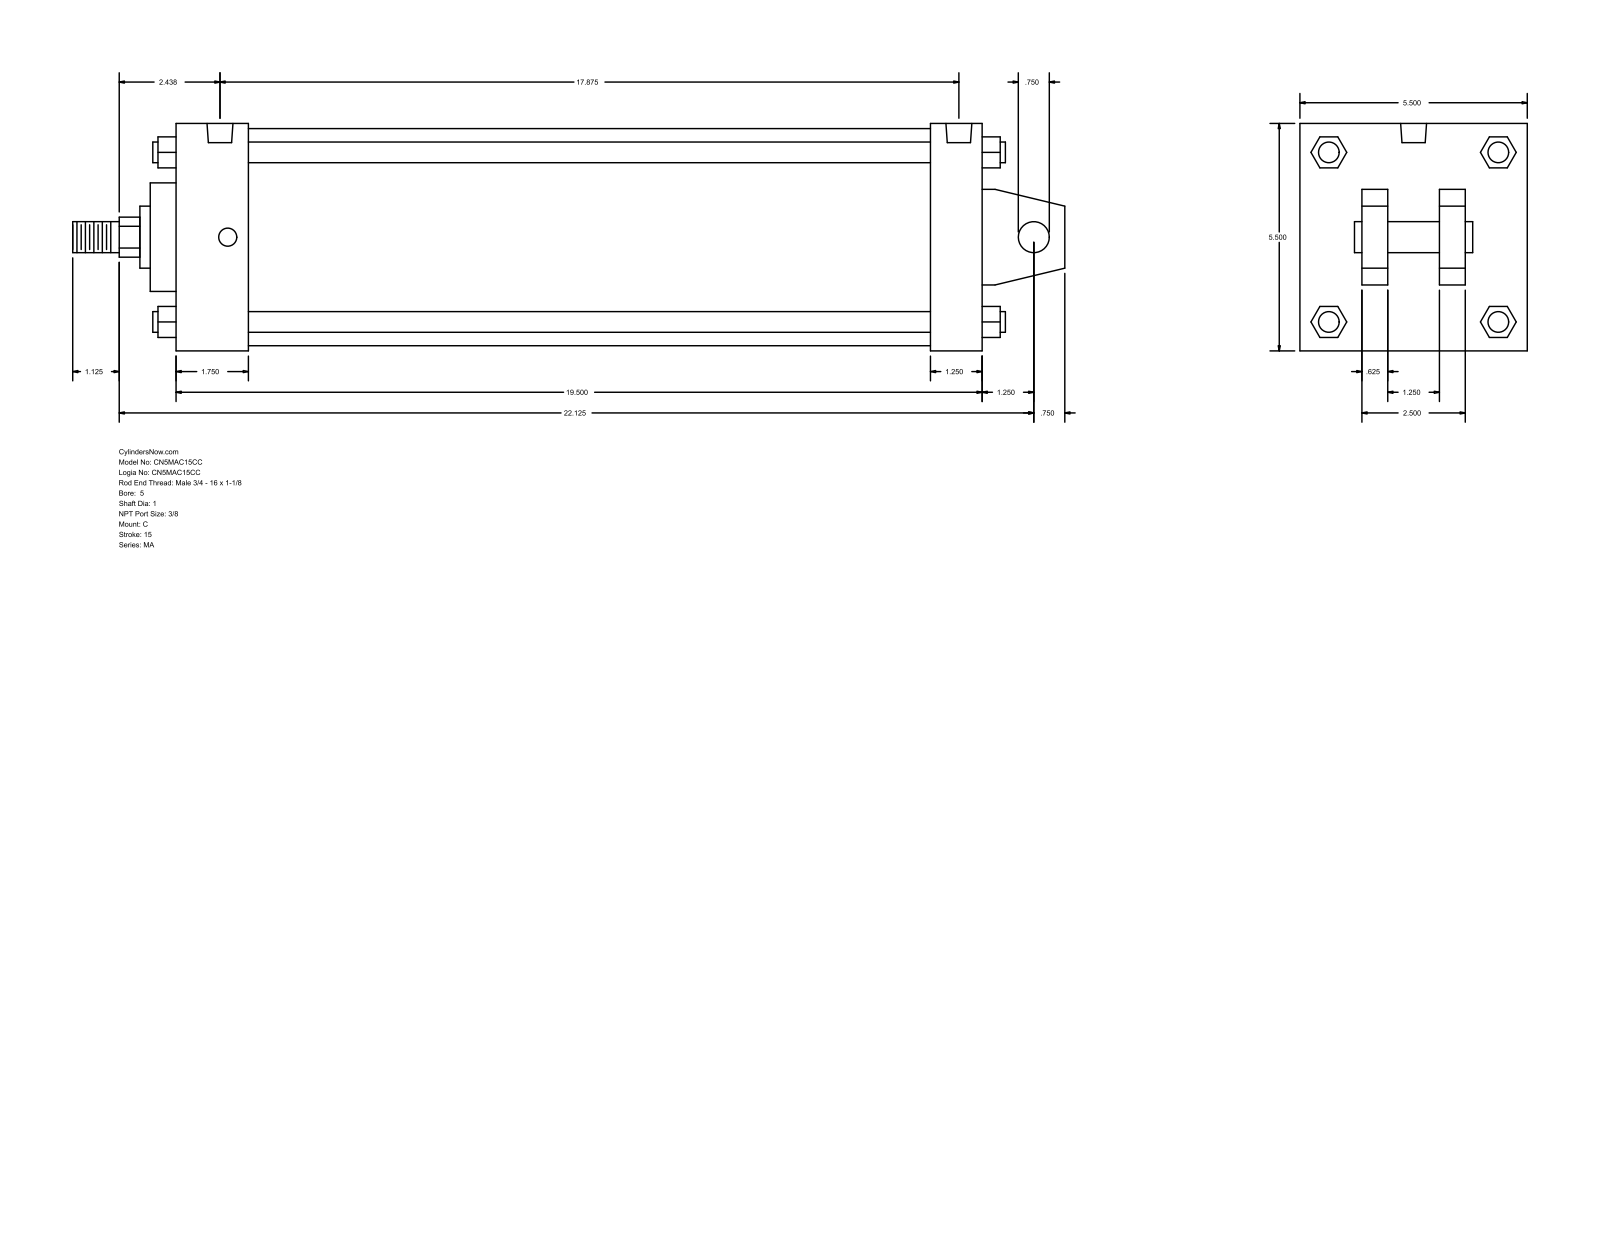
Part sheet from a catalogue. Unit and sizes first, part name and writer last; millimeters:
Units: millimetres
Overall size (bounding box): 609.6 × 139.7 × 139.7
Round holes (diameter × count): ⌀11.11 ×4, ⌀15.93 ×2
Round bosses / shafts (diameter × count): ⌀12.7 ×4, ⌀19.05 ×2, ⌀133.35 ×1, ⌀66.67 ×1, ⌀38.1 ×1, ⌀25.4 ×1
Partial cylindrical surfaces — rounded edges, fillets, slot ends (radius × count): R12.29 ×1
Main face-to-face distances: 139.7, 495.31, 15.87, 463.56, 31.75, 44.46, 419.1, 450.85, 38.1, 101.6
Hole centre spacings: 4.76, 444.51, 449.27, 454.03
Bodies: 0 solids, 141 faces (109 planar, 32 cylindrical, 0 other)
Part name (STEP PRODUCT): MA_C__0500_1
STEP written by: GSSL Pune (CONFIG_CONTROL_DESIGN)
